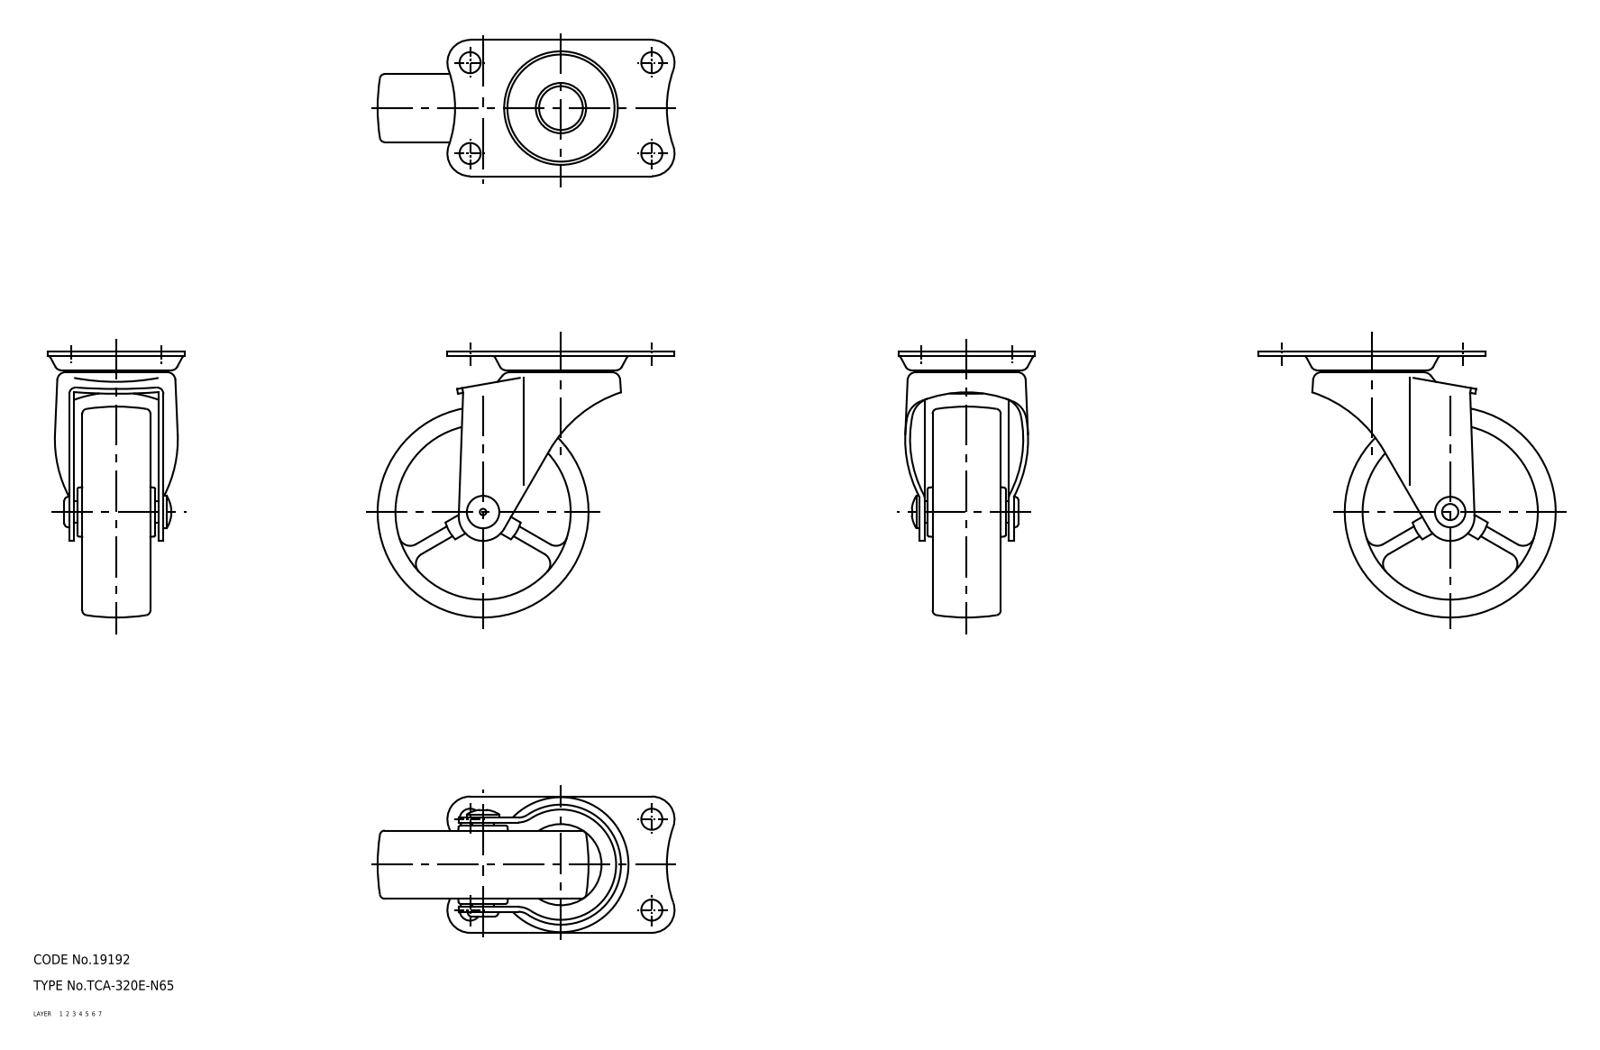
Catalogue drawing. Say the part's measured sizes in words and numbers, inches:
The part is named "wheel; mounting plate; main shaft; axle (+1 more)". Its 3-D file was written by "CADfix (AUTOMOTIVE_DESIGN)". It is 5 solids with 420 faces: 0 planar, 0 cylindrical and 420 other. Overall it measures 3.602 by 3.228 by 1.654 inches. Its volume is 3.922 cubic inches and its surface area 48.99 square inches.
